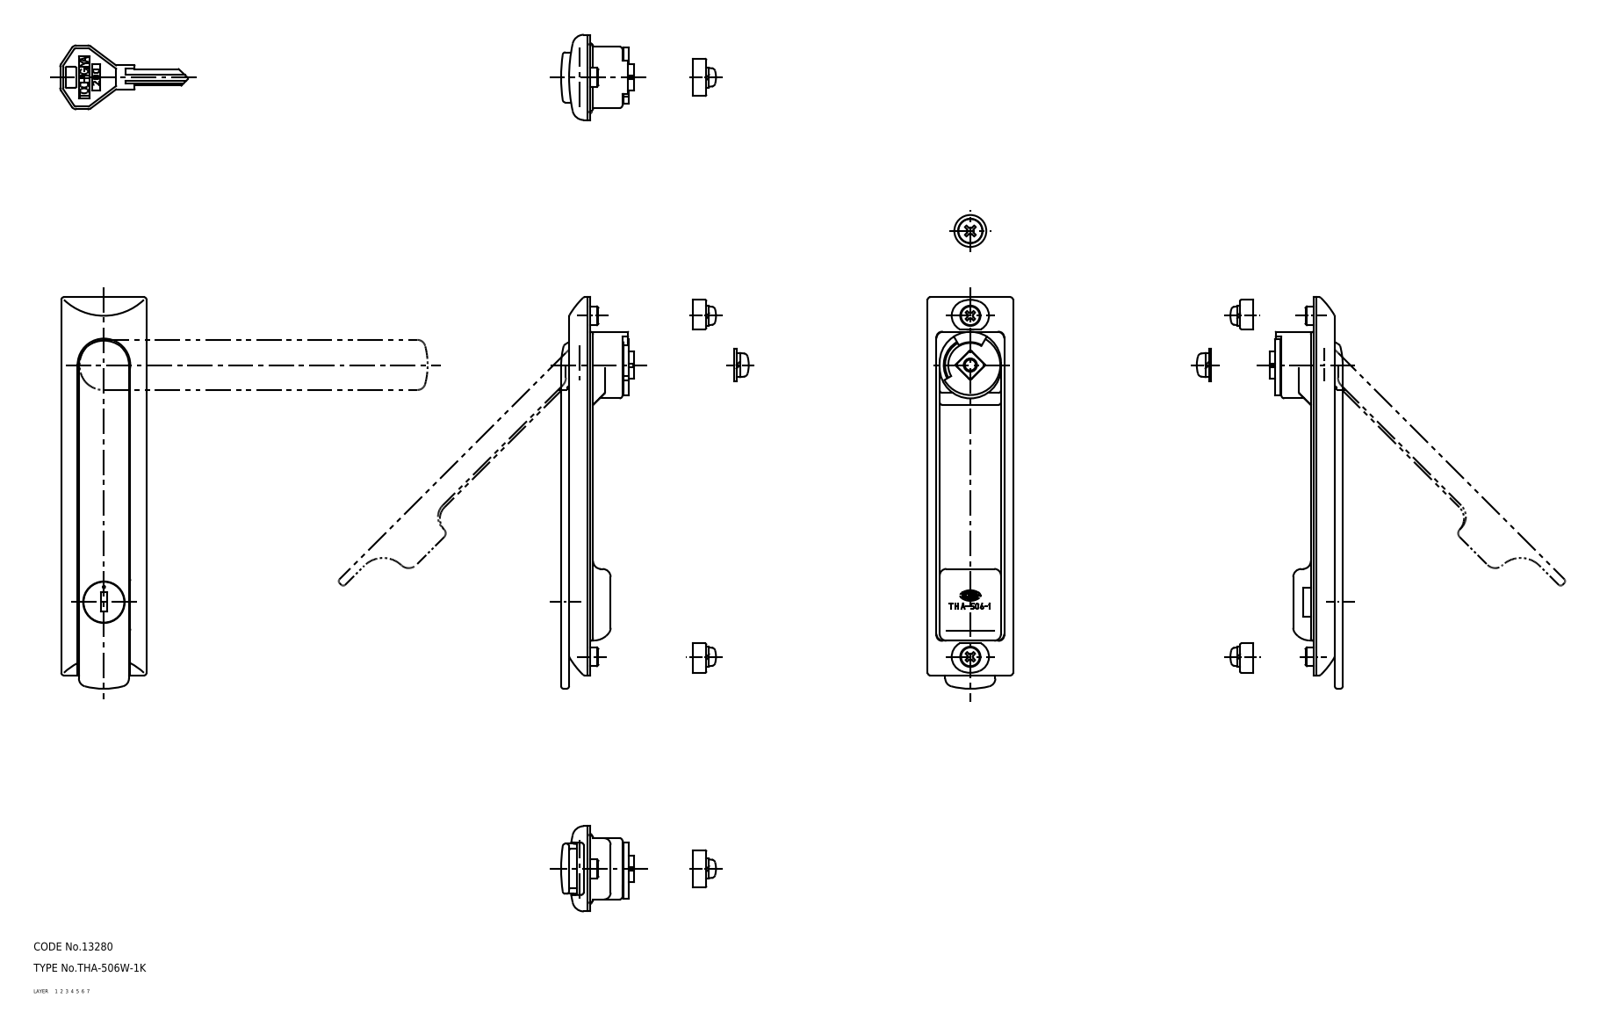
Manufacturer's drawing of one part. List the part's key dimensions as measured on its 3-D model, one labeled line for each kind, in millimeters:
Part name (STEP PRODUCT): packing; screw_A; bracket; shaft_B (+8 more)
STEP written by: CADfix (AUTOMOTIVE_DESIGN)
Units: millimetres
Bodies: 13 solids, 462 faces (0 planar, 0 cylindrical, 462 other)
Overall size (bounding box): 147 × 93.27 × 32
Volume: 43 020 mm³ · Surface area: 35 283 mm²
